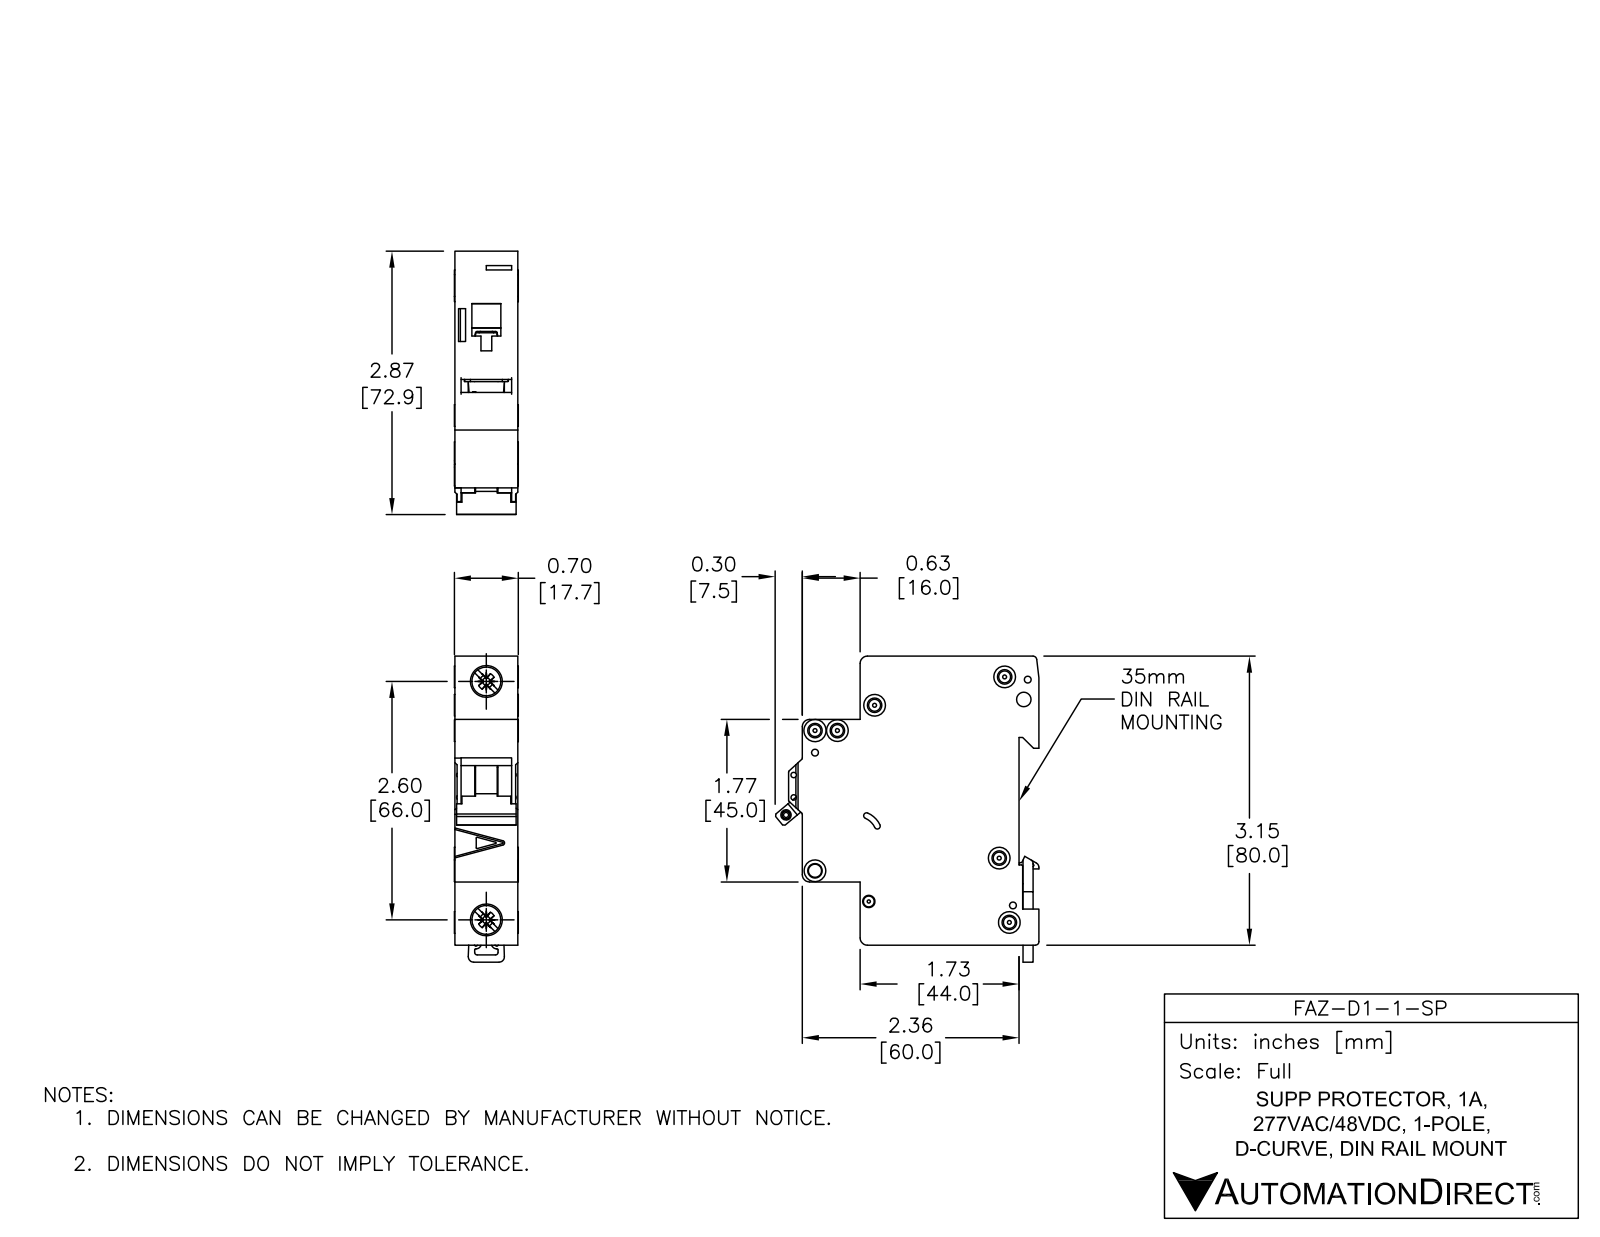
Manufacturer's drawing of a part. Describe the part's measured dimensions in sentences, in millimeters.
The part is named "FAZ-D1-1-SP". Its 3-D file was written by "SolidWorks 2014 (AUTOMOTIVE_DESIGN)". It is 5 solids with 558 faces: 235 planar, 202 cylindrical and 121 other. Overall it measures 84.78 by 73.04 by 17.7 millimeters. Its volume is 74 935 cubic millimeters and its surface area 19 545 square millimeters. Round holes: 6 of diameter 3.6, 3 of diameter 1.9, 2 of diameter 1.09, 2 of diameter 1.5, 2 of diameter 4, 2 of diameter 7.15, 1 of diameter 2.15, 1 of diameter 2.2, 1 of diameter 2.55, 1 of diameter 3.3, 1 of diameter 3.4. Round bosses or shafts: 4 of diameter 6, 2 of diameter 8.2, 1 of diameter 2.5. Partial cylindrical surfaces (rounded edges, fillets, slot ends): 30 of radius 0.25, 13 of radius 0.5, 8 of radius 2, 5 of radius 0.2, 4 of radius 1, 2 of radius 0.8, 2 of radius 3, 1 of radius 1.5. The main face-to-face distances are 17.5, 79.48, 5.5, 49.5, 44, 65.5, 60, 16, 1.75, 15.75. The hole center spacings are 6.2, 13.64, 4.81, 5.19, 5.61, 6.1, 6.44, 8.19.
